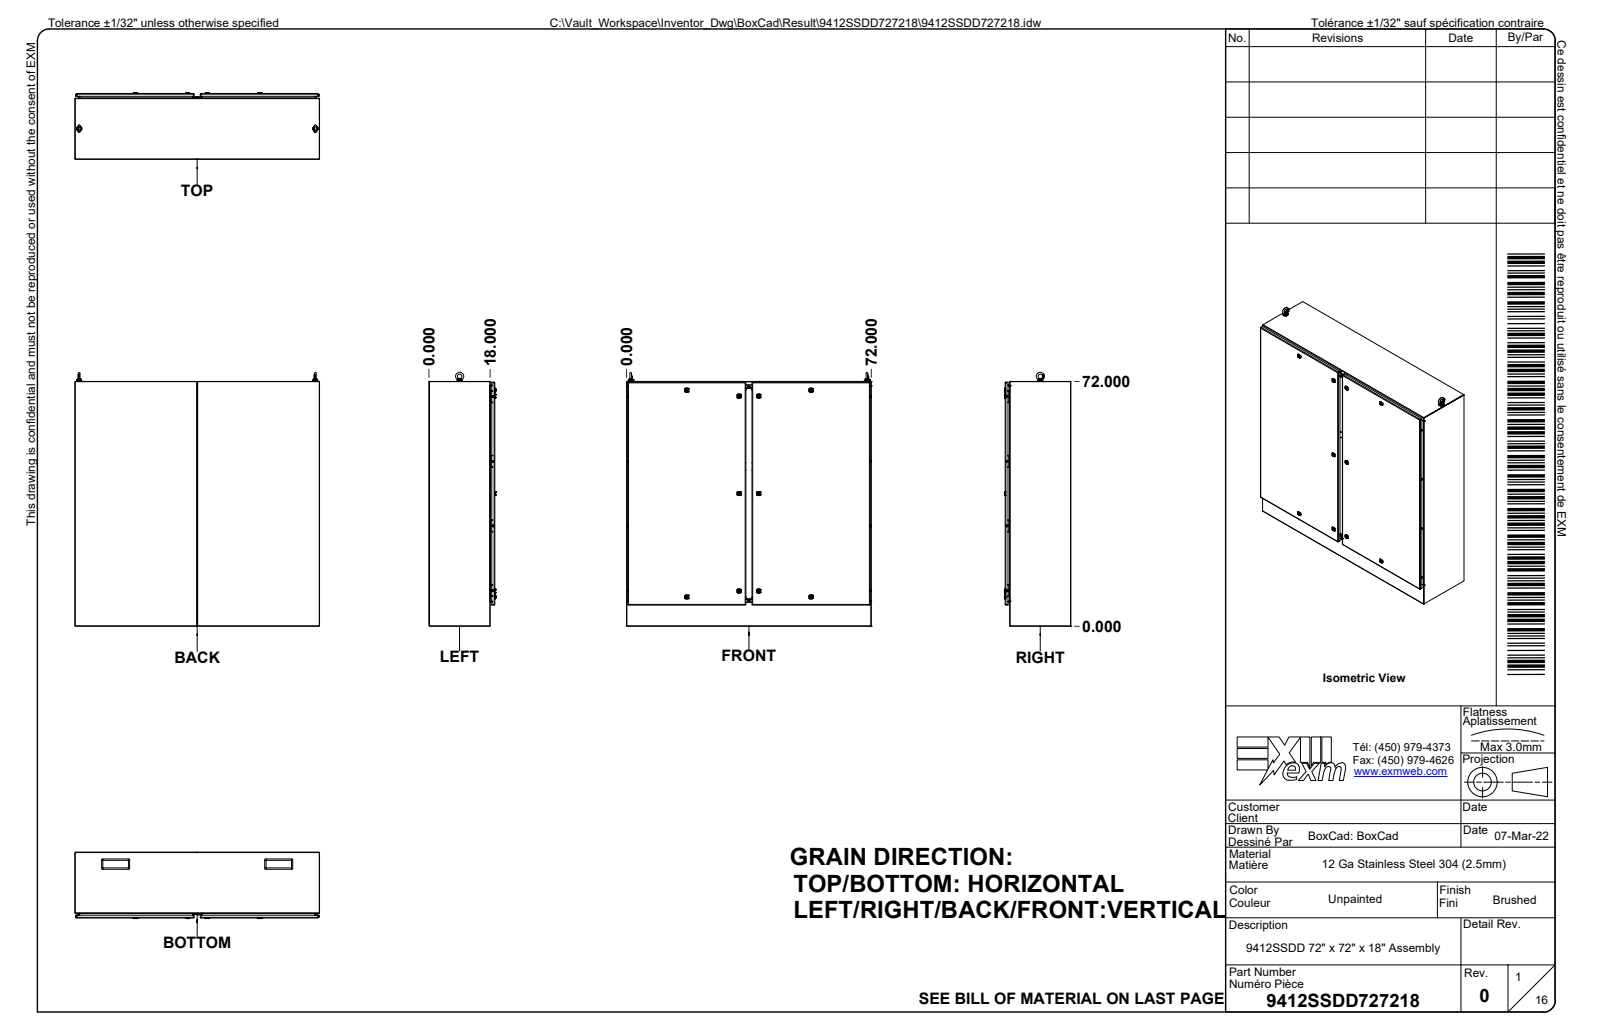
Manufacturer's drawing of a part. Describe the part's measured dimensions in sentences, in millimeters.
The part is named "9412SSDD727218; 9412SSDD727218B; 9412SSDD727218BL-P; 9412SSDD727218BR-P (+8 more)". Its 3-D file was written by "Autodesk Inventor 2024 (AUTOMOTIVE_DESIGN)". It is 373 solids with 45960 faces: 20726 planar, 10116 cylindrical and 15118 other. Overall it measures 1895.8 by 1828.8 by 495.5 millimeters. Its volume is 32 000 000 cubic millimeters and its surface area 24 300 000 square millimeters. Round holes: 33 of diameter 5.1, 23 of diameter 0.8, 17 of diameter 8, 13 of diameter 5, 13 of diameter 6.8, 12 of diameter 3, 10 of diameter 7.9, 10 of diameter 10, 10 of diameter 16, 10 of diameter 20.6, 10 of diameter 29, 8 of diameter 6. Round bosses or shafts: 56 of diameter 5.9, 23 of diameter 0.8, 17 of diameter 19.5, 15 of diameter 9.9, 14 of diameter 12, 13 of diameter 9.5, 12 of diameter 1.3, 11 of diameter 6. Partial cylindrical surfaces (rounded edges, fillets, slot ends): 1809 of radius 0.5, 932 of radius 1, 552 of radius 0.2, 240 of radius 0.3, 240 of radius 2, 236 of radius 0.3, 162 of radius 3, 134 of radius 0.8. The main face-to-face distances are 2.7, 1826.1, 2.7, 488.5, 485.9, 491.2, 488.5, 1823.5, 1828.8, 454.5. The hole center spacings are 482.6, 482.8, 11.8, 12, 12.5, 21.1, 30.5, 32.4.
